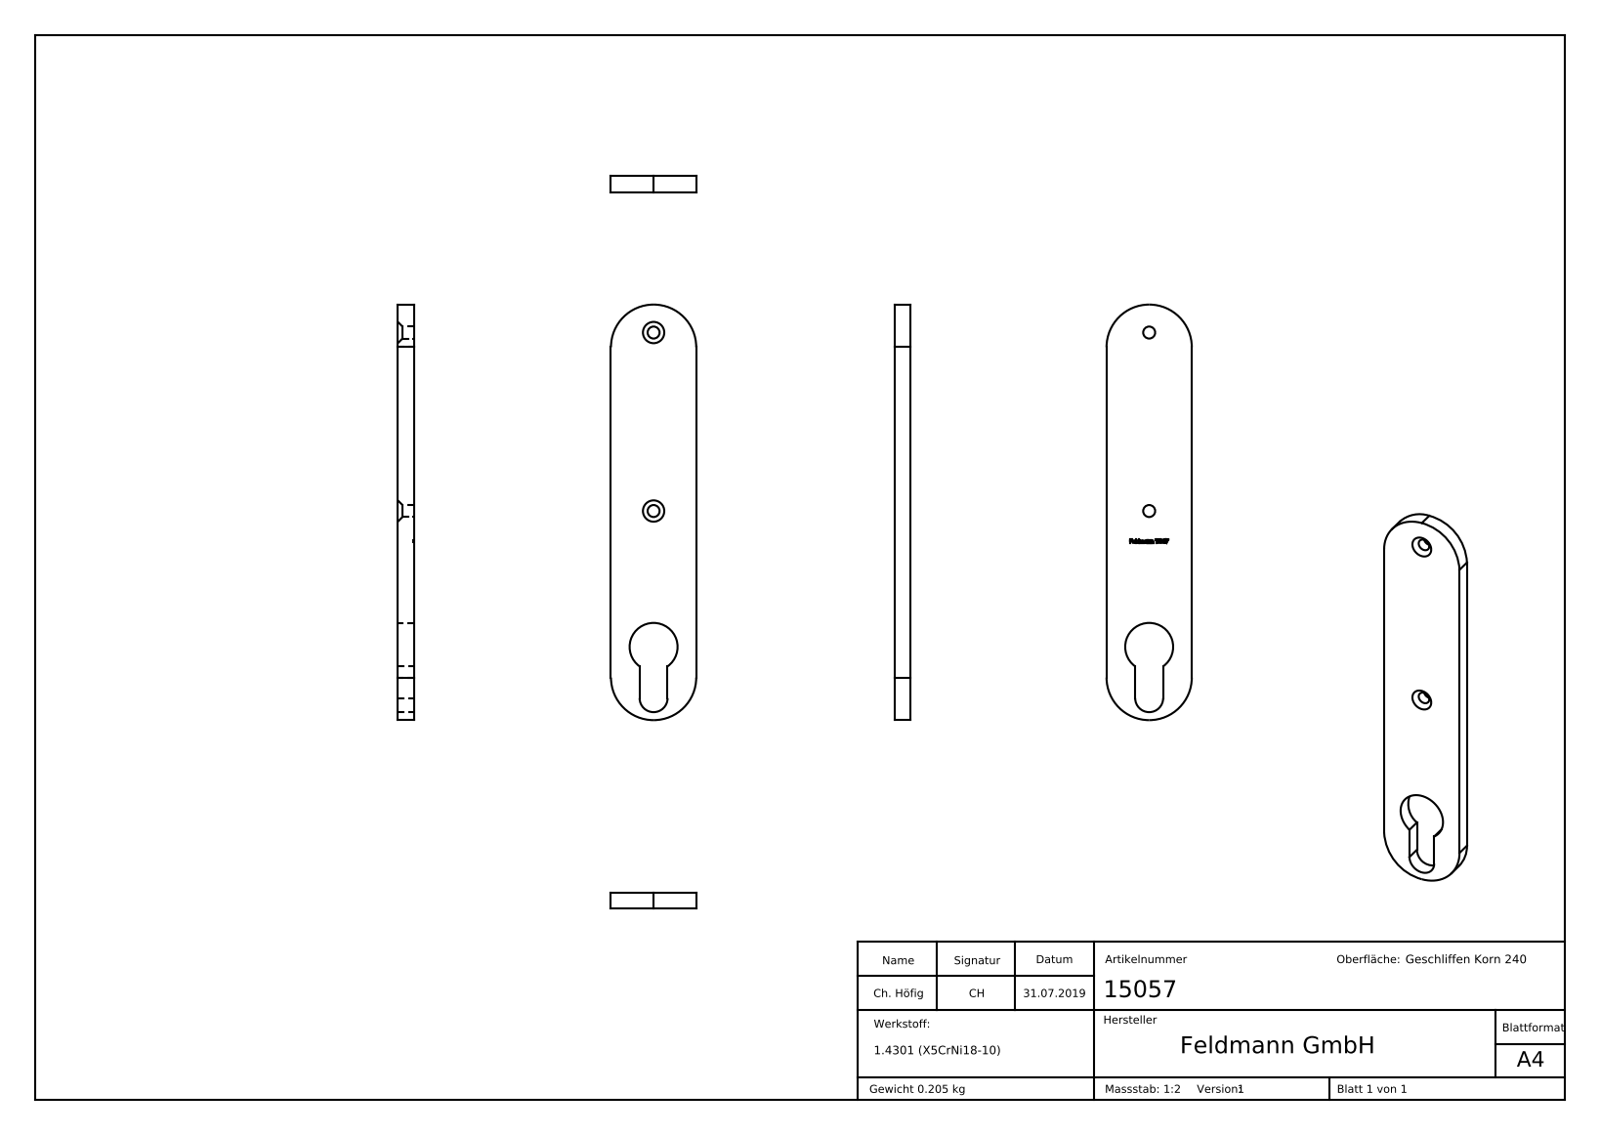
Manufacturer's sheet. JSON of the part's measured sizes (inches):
{"part_name": "15057", "step_written_by": "SolidWorks 2015 (CONFIG_CONTROL_DESIGN)", "units": "inches", "bodies": {"solids": 1, "faces": 190, "planar": 101, "cylindrical": 12, "other": 77}, "overall_size": [6.142, 1.26, 0.236], "volume_in3": 1.582, "surface_area_in2": 17.7, "round_holes": [[0.177, 2], [0.709, 1]], "partial_cylinders_radius": [[0.63, 2], [0.207, 1]], "face_to_face_distances": [0.236, 1.26, 0.423, 0.837, 0.413, 0.232, 0.117, 0.072, 0.015, 0.302], "hole_center_spacings": [2.008, 2.638, 4.646]}
